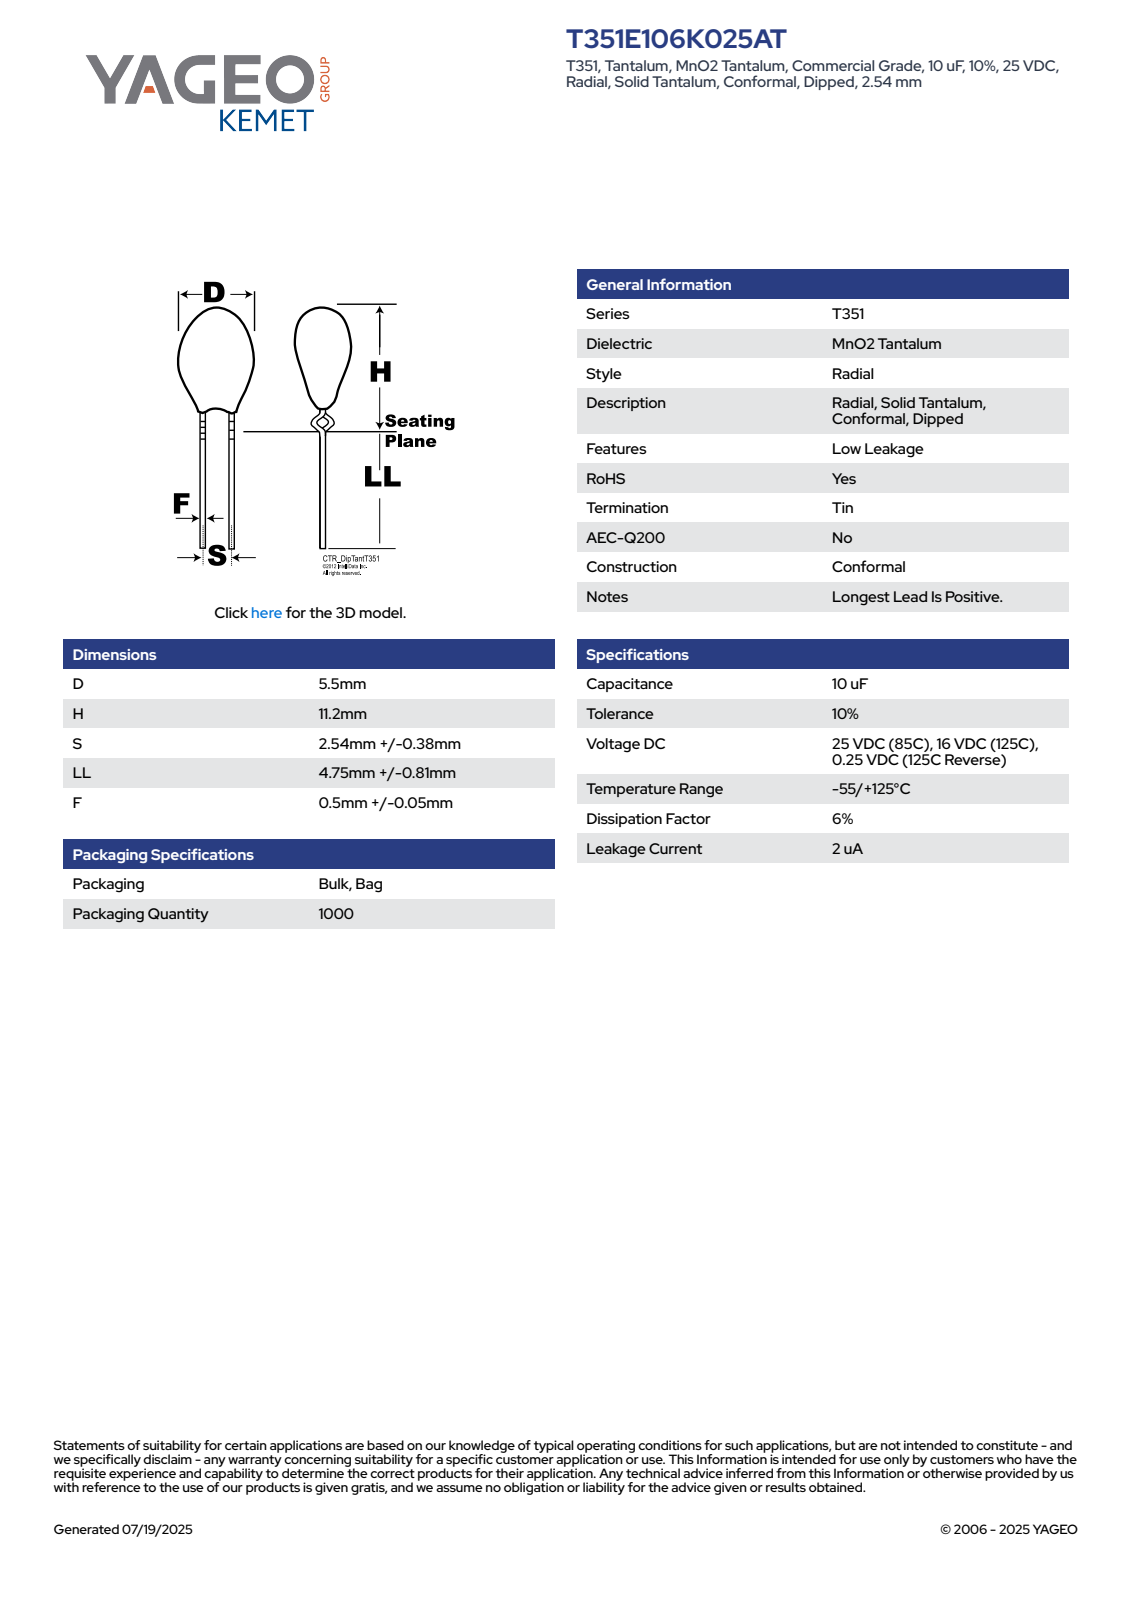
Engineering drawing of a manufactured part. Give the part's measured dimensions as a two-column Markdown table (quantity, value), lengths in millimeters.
| quantity | value |
| --- | --- |
| part name | CTR_T351_D5.5H11.2S2.54LL5.56F0.55 |
| STEP written by | SolidWorks 2014 (AUTOMOTIVE_DESIGN) |
| units | millimeters |
| bodies | 1 solid, 87 faces (27 planar, 9 cylindrical, 51 other) |
| overall size | 16.76 × 5.5 × 5.5 |
| volume | 159 mm³ |
| surface area | 179 mm² |
| round bosses / shafts (diameter × count) | 0.55 × 2, 5.5 × 1 |
| partial cylindrical surfaces (radius × count) | 2.74 × 1 |
| main face-to-face distances | 8.59, 12.85, 4.26, 12.04, 3.45, 0.81, 12.2, 3.61, 0.65, 16.76 |
